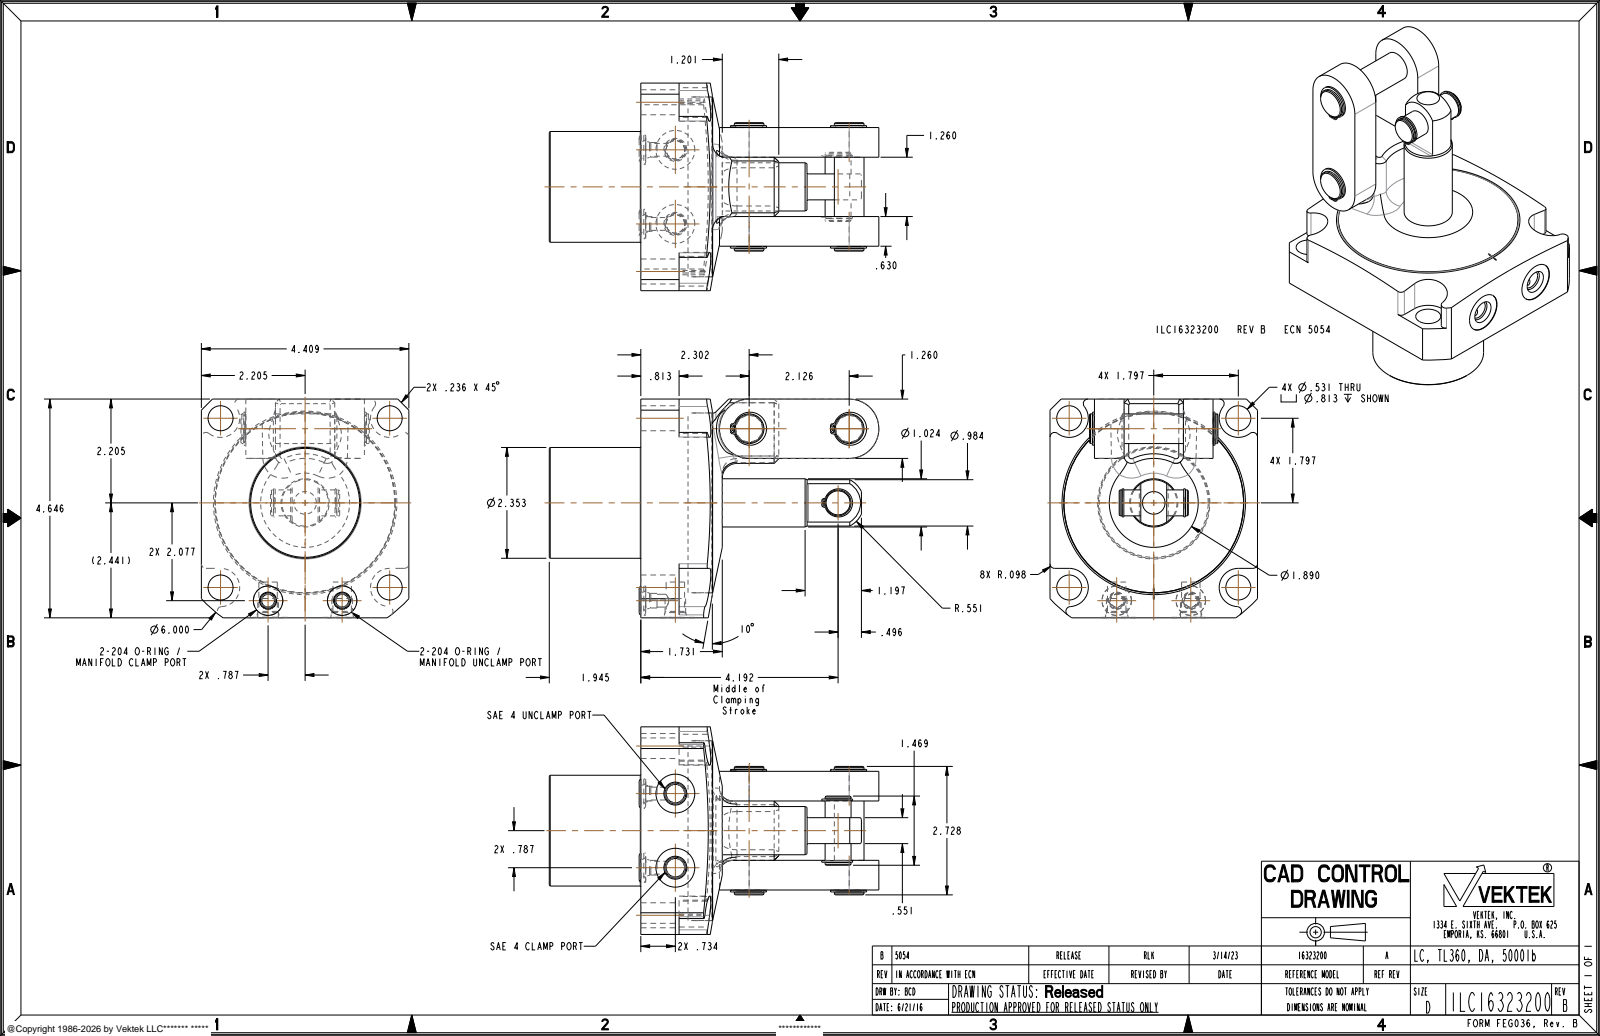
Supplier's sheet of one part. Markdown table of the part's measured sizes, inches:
| quantity | value |
| --- | --- |
| part name | ILC16323200_BODY; ILC16323200_LUG; ILC16323200 |
| STEP written by | CREO PARAMETRIC BY PTC INC, 2021164 (AUTOMOTIVE_DESIGN) |
| units | inches |
| bodies | 2 solids, 338 faces (106 planar, 169 cylindrical, 63 other) |
| overall size | 7.003 × 4.646 × 4.409 |
| volume | 47.61 in³ |
| surface area | 168.1 in² |
| round holes (diameter × count) | 0.047 × 6, 0.531 × 4, 0.272 × 2, 0.392 × 2, 0.579 × 2, 0.625 × 2, 0.825 × 2, 3.82 × 1 |
| round bosses / shafts (diameter × count) | 0.702 × 2, 0.63 × 2, 0.559 × 2, 0.437 × 2, 0.31 × 2, 3.816 × 1, 2.353 × 1, 1.024 × 1 |
| partial cylindrical surfaces (radius × count) | 0.098 × 8, 0.047 × 6, 0.031 × 4, 0.05 × 4, 0.406 × 4, 0.034 × 2, 0.157 × 2, 0.63 × 2 |
| main face-to-face distances | 1.003, 0.944, 3.464, 4.409, 1.574, 2.834, 0.63, 1.89, 1.945, 2.948 |
| hole center spacings | 0.356, 2.541, 3.594, 2.126, 1.048, 1.574, 1.777, 2.13 |
